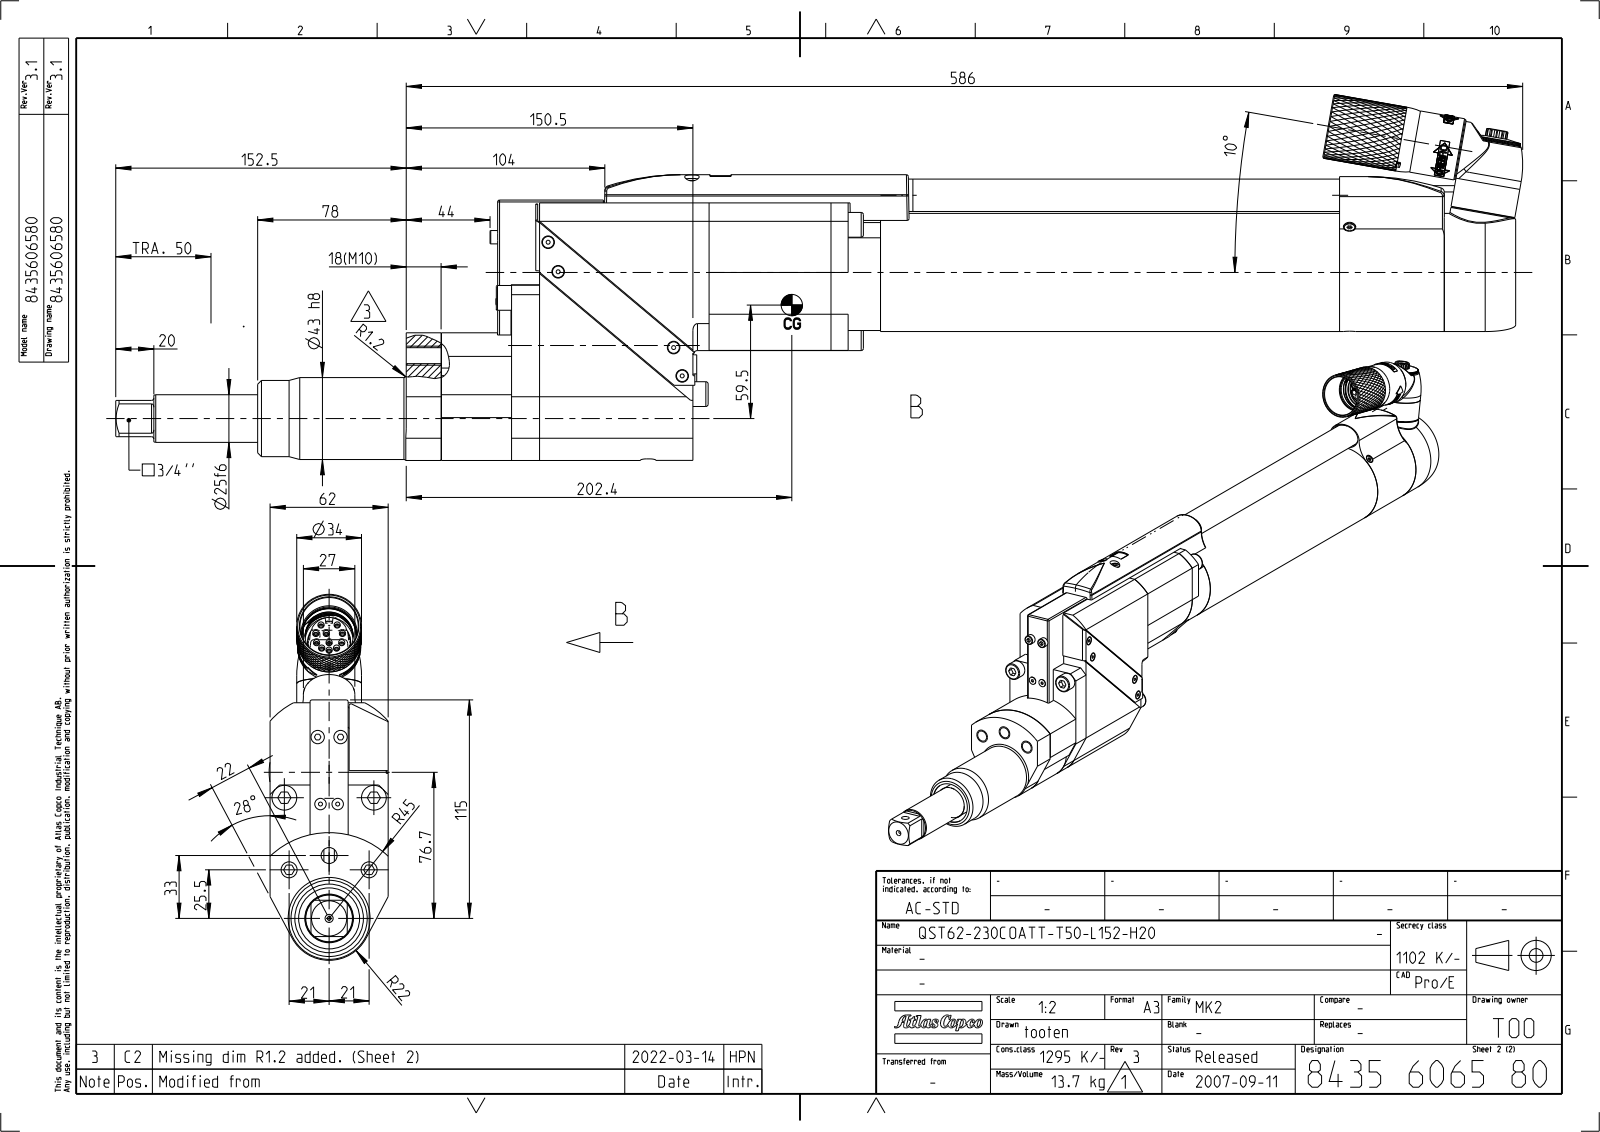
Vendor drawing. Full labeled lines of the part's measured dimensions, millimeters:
Part name (STEP PRODUCT): 8435606580_ASM_SW0001
STEP written by: CREO PARAMETRIC BY PTC INC, 2022414 (AP242_MANAGED_MODEL_BASED_3D_ENGINEERING_MIM_LF)
Units: millimetres
Bodies: 1 solid, 2120 faces (964 planar, 427 cylindrical, 729 other)
Overall size (bounding box): 738.6 × 192 × 62.5
Volume: 2 461 000 mm³ · Surface area: 273 700 mm²
Round holes (diameter × count): ⌀3.3 ×4, ⌀4.5 ×4, ⌀11 ×4, ⌀6.5 ×3, ⌀8.4 ×3, ⌀2.5 ×2, ⌀2.9 ×2, ⌀3.3 ×2, ⌀4.9 ×2, ⌀6.4 ×2, ⌀6.7 ×2, ⌀1 ×1
Round bosses / shafts (diameter × count): ⌀13 ×7, ⌀6 ×7, ⌀7 ×4, ⌀4 ×4, ⌀3 ×4, ⌀34 ×3, ⌀5.6 ×2, ⌀62 ×1
Partial cylindrical surfaces — rounded edges, fillets, slot ends (radius × count): R1 ×13, R0.3 ×12, R0.5 ×12, R0.5 ×11, R2 ×7, R1.2 ×4, R3 ×4, R4 ×4
Main face-to-face distances: 62, 1, 21, 22, 41, 40, 5.5, 19, 20, 512.5
Hole centre spacings: 12, 47, 12.9, 12.9, 22.3, 22.8, 26.8, 26.8
